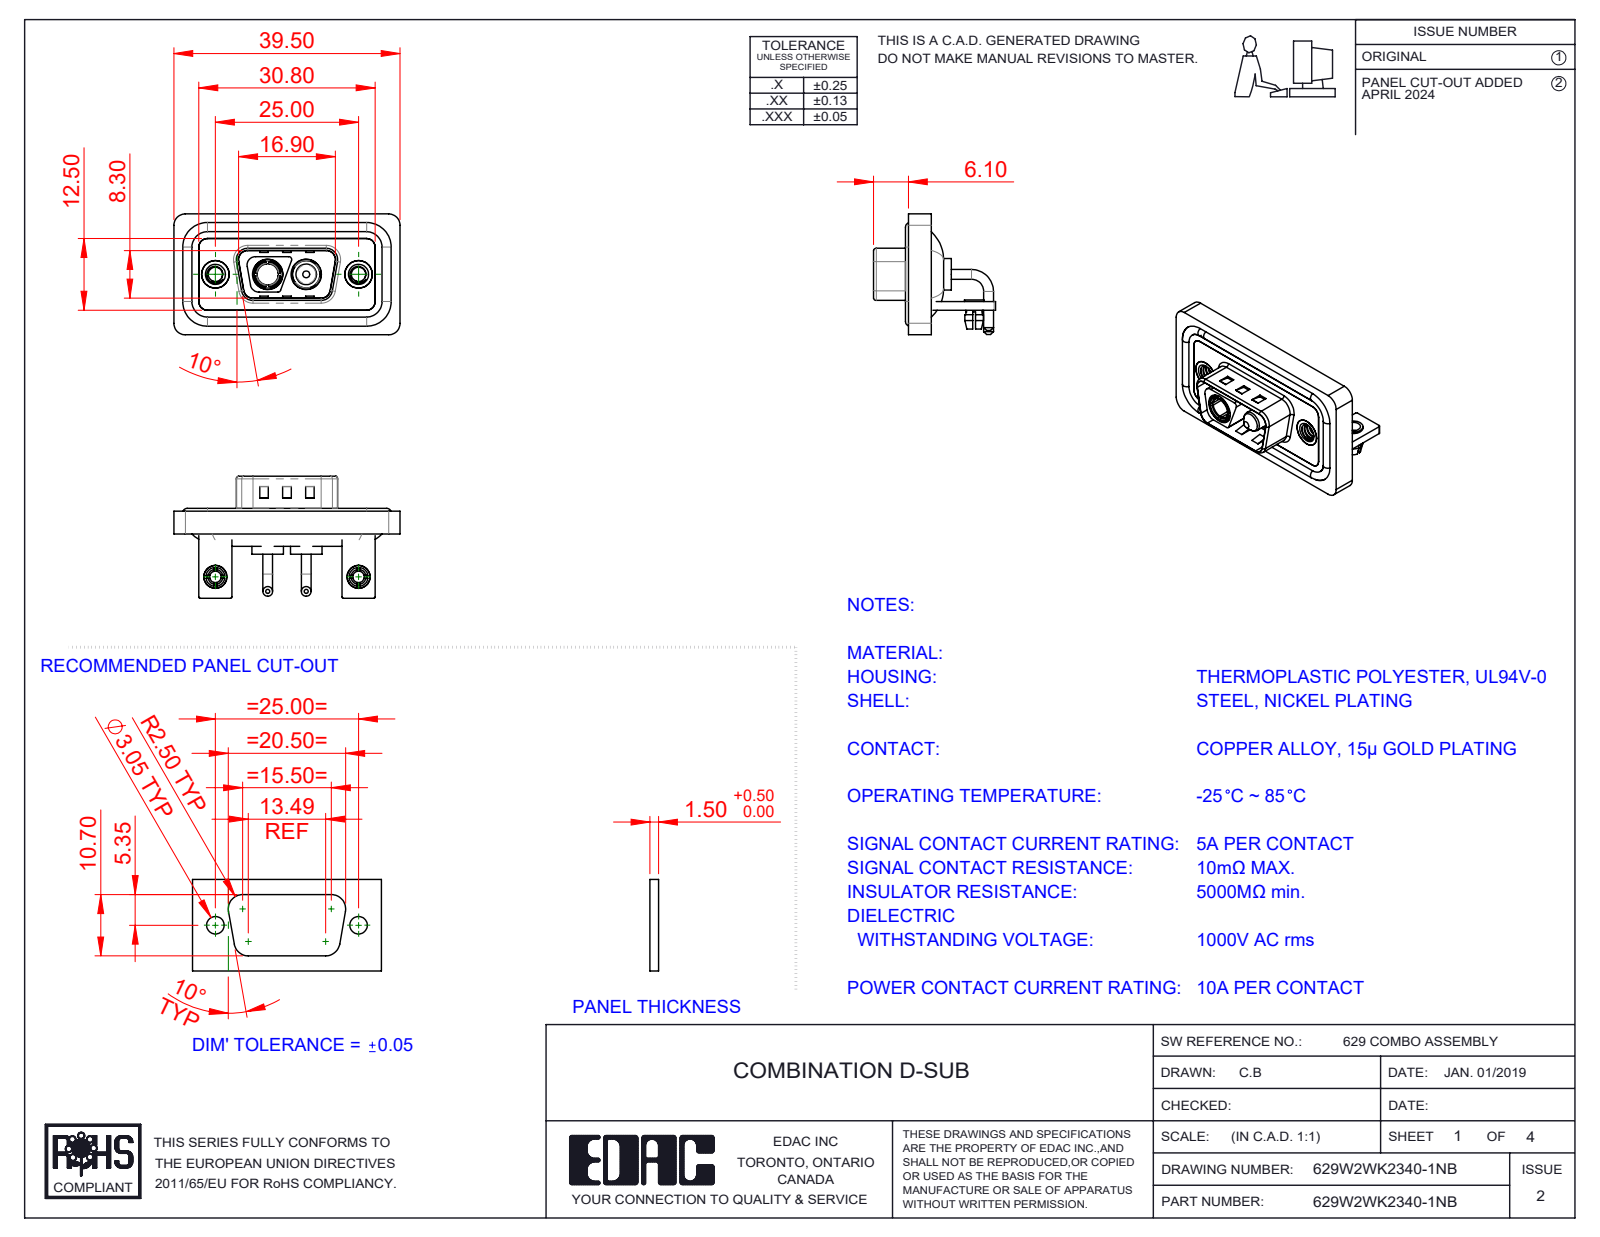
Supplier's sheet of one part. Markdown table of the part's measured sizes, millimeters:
| quantity | value |
| --- | --- |
| part name | 629Combo Stabilizer Bracket; Power Pin_10A RA; 629Combo Board Lock; 629Combo Threaded Rivet_B (+6 more) |
| STEP written by | SolidWorks 2023 (CONFIG_CONTROL_DESIGN) |
| units | millimeters |
| bodies | 15 solids, 672 faces (257 planar, 281 cylindrical, 134 other) |
| overall size | 39.5 × 21.3 × 21.1 |
| volume | 4 872 mm³ |
| surface area | 8 226 mm² |
| round holes (diameter × count) | 2.5 × 4, 2 × 2, 3.2 × 2, 4 × 2, 4.8 × 2, 4.85 × 2, 5 × 2, 5.3 × 2, 3.7 × 1 |
| round bosses / shafts (diameter × count) | 1.7 × 4, 1.6 × 4, 5.5 × 2, 5.2 × 2, 4.9 × 2, 4.75 × 2, 4 × 2, 3.75 × 2 |
| partial cylindrical surfaces (radius × count) | 1.5 × 20, 2 × 19, 0.25 × 16, 0.5 × 11, 1.6 × 8, 0.6 × 4, 0.65 × 4, 0.9 × 4 |
| main face-to-face distances | 0.4, 1.5, 2.9, 0.8, 1.1, 1.2, 2.1, 1.6, 3.7, 2.5 |
| hole center spacings | 9.14, 15.86, 25, 6.72 |
